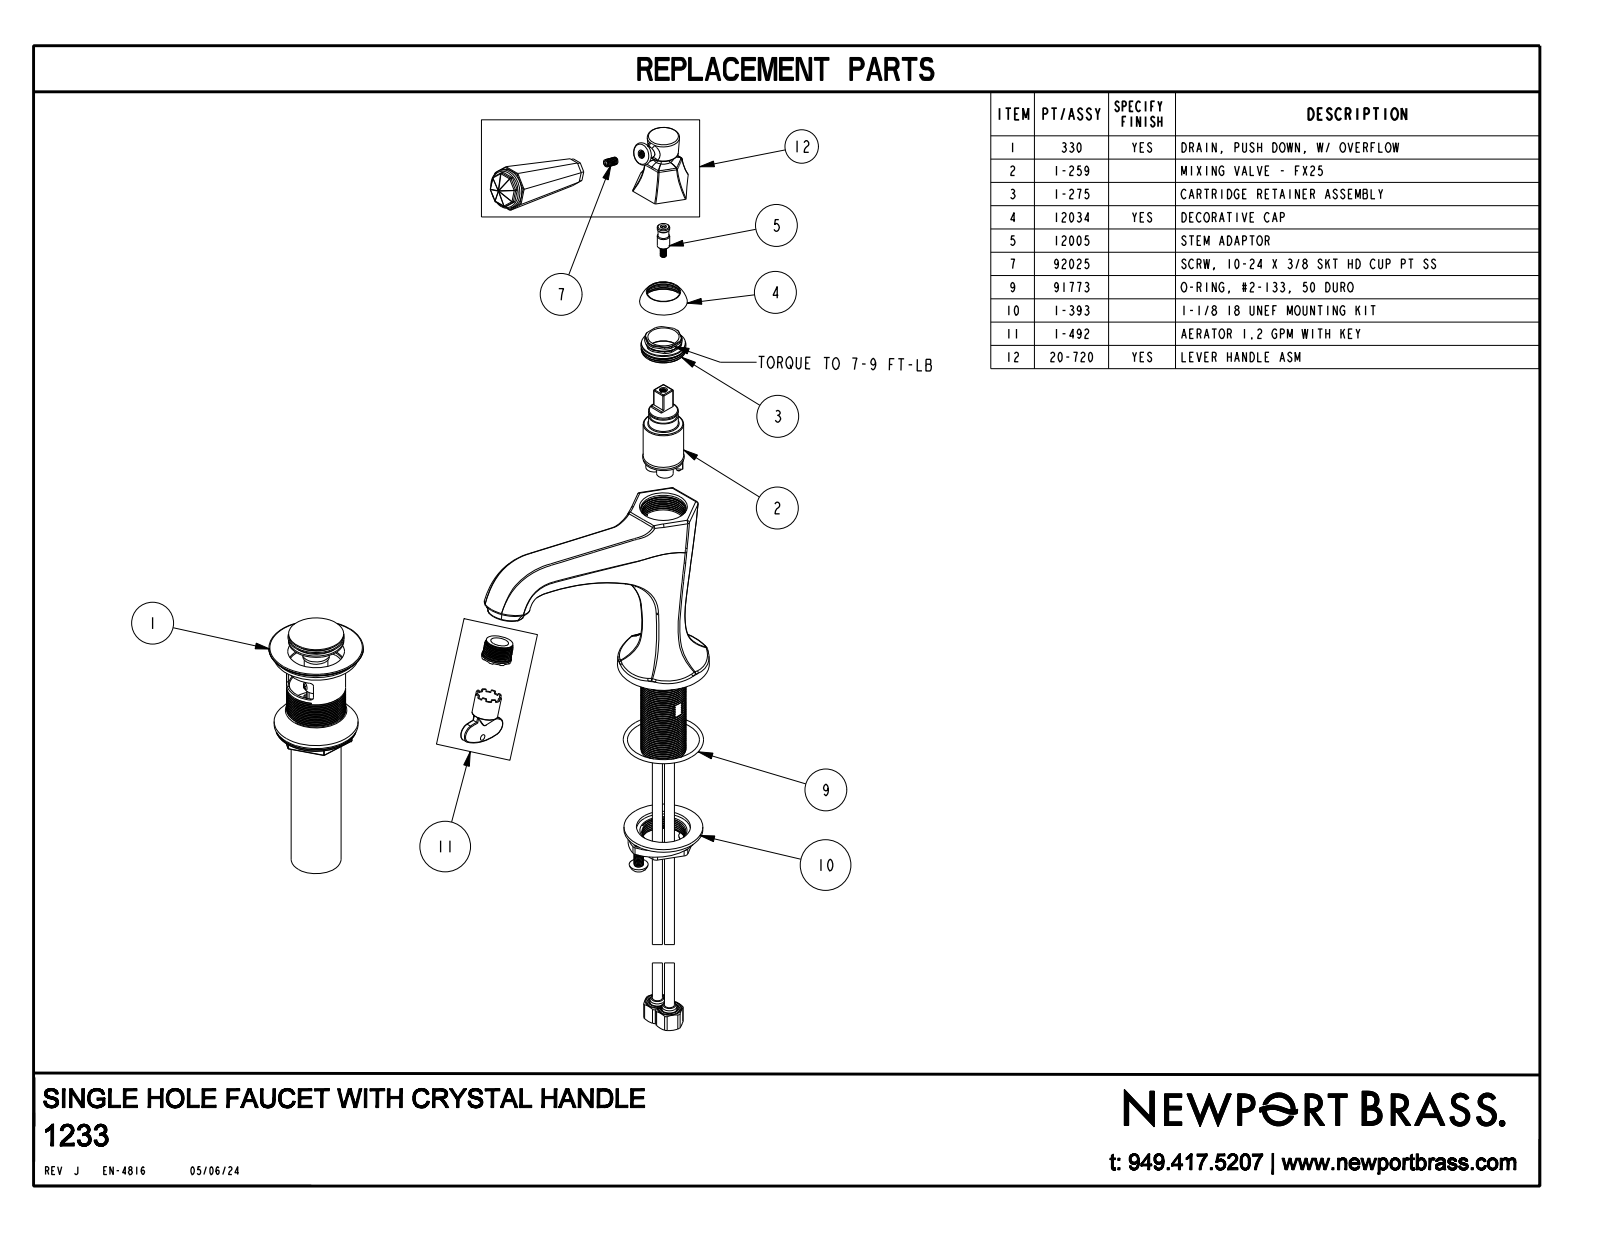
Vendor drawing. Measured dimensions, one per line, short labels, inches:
name: 1233
written by: CREO PARAMETRIC BY PTC INC, 2018400 (AUTOMOTIVE_DESIGN)
unit: in
bodies: 2 solids, 332 faces (72 planar, 33 cylindrical, 227 other)
size: 7.391 × 7.236 × 2.3
volume: 15.94 in³; area: 67.81 in²
holes: 1× ⌀1.135
bosses: 1× ⌀0.98
rounds: 24× R0.03, 5× R0.06
face distances: 4.809, 0.1, 4.709, 4.872, 0.163, 0.063, 0.354, 5.602, 0.893, 0.793
